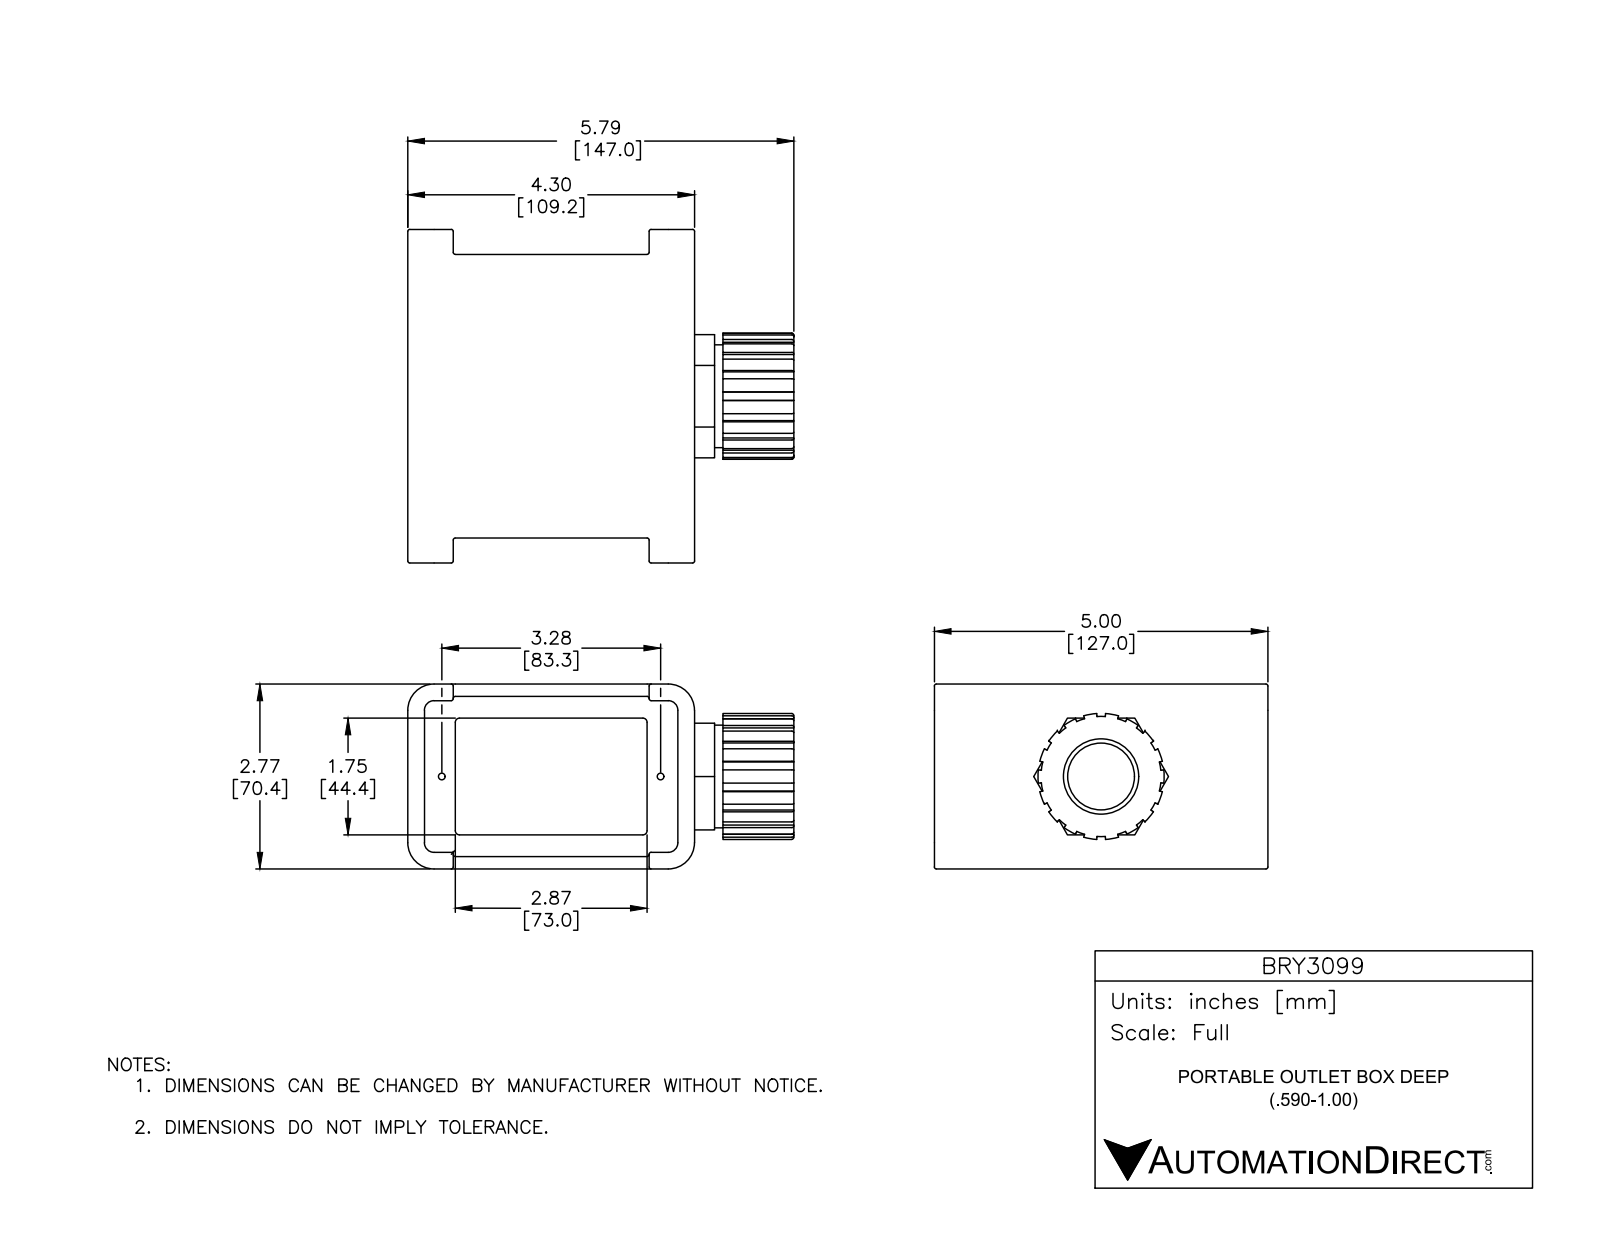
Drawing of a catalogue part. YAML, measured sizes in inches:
part_name: "BRY3099"
step_written_by: "SolidWorks 2016 (AUTOMOTIVE_DESIGN)"
units: inches
bodies: {solids: 3, faces: 382, planar: 101, cylindrical: 174, other: 107}
overall_size: [5.787, 5, 2.772]
volume: 29.24
surface_area: 151.3
round_holes:
  - {diameter: 0.1, count: 2}
  - {diameter: 1, count: 1}
  - {diameter: 1.13, count: 1}
  - {diameter: 1.58, count: 1}
round_bosses_or_shafts:
  - {diameter: 1.54, count: 1}
partial_cylinders:
  - {radius: 0.03, count: 68}
  - {radius: 0.062, count: 4}
  - {radius: 0.144, count: 4}
  - {radius: 0.394, count: 4}
  - {radius: 0.9, count: 1}
  - {radius: 0.946, count: 1}
face_to_face_distances: [0.511, 2.261, 2.772, 0.712, 3.587, 1.75, 4.299, 0.25, 2.875, 4.049]
hole_center_spacings: [3.28]
